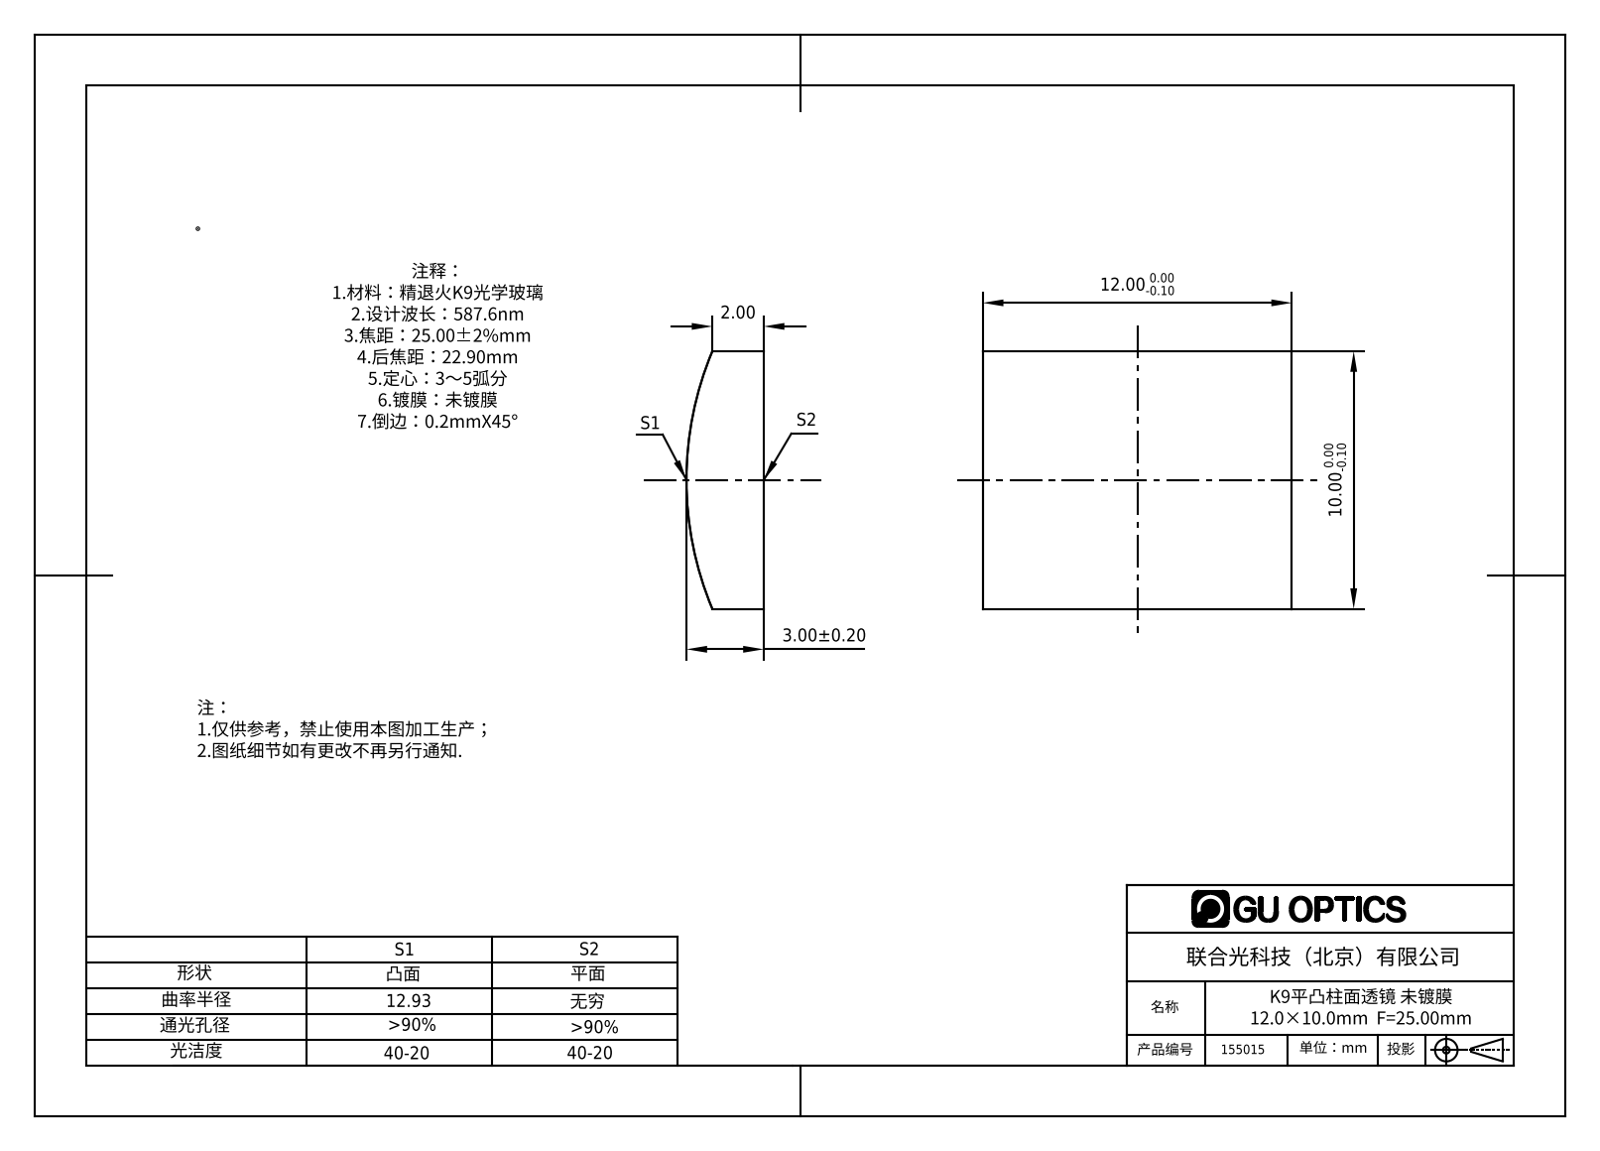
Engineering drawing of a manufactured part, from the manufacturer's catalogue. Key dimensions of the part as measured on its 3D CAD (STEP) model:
Part name (STEP PRODUCT): 155015
STEP written by: SolidWorks 2016 (AUTOMOTIVE_DESIGN)
Units: millimetres
Bodies: 1 solid, 6 faces (5 planar, 1 cylindrical, 0 other)
Overall size (bounding box): 12 × 10 × 3
Volume: 320 mm³ · Surface area: 344 mm²
Partial cylindrical surfaces — rounded edges, fillets, slot ends (radius × count): R12.93 ×1
Main face-to-face distances: 12, 10
